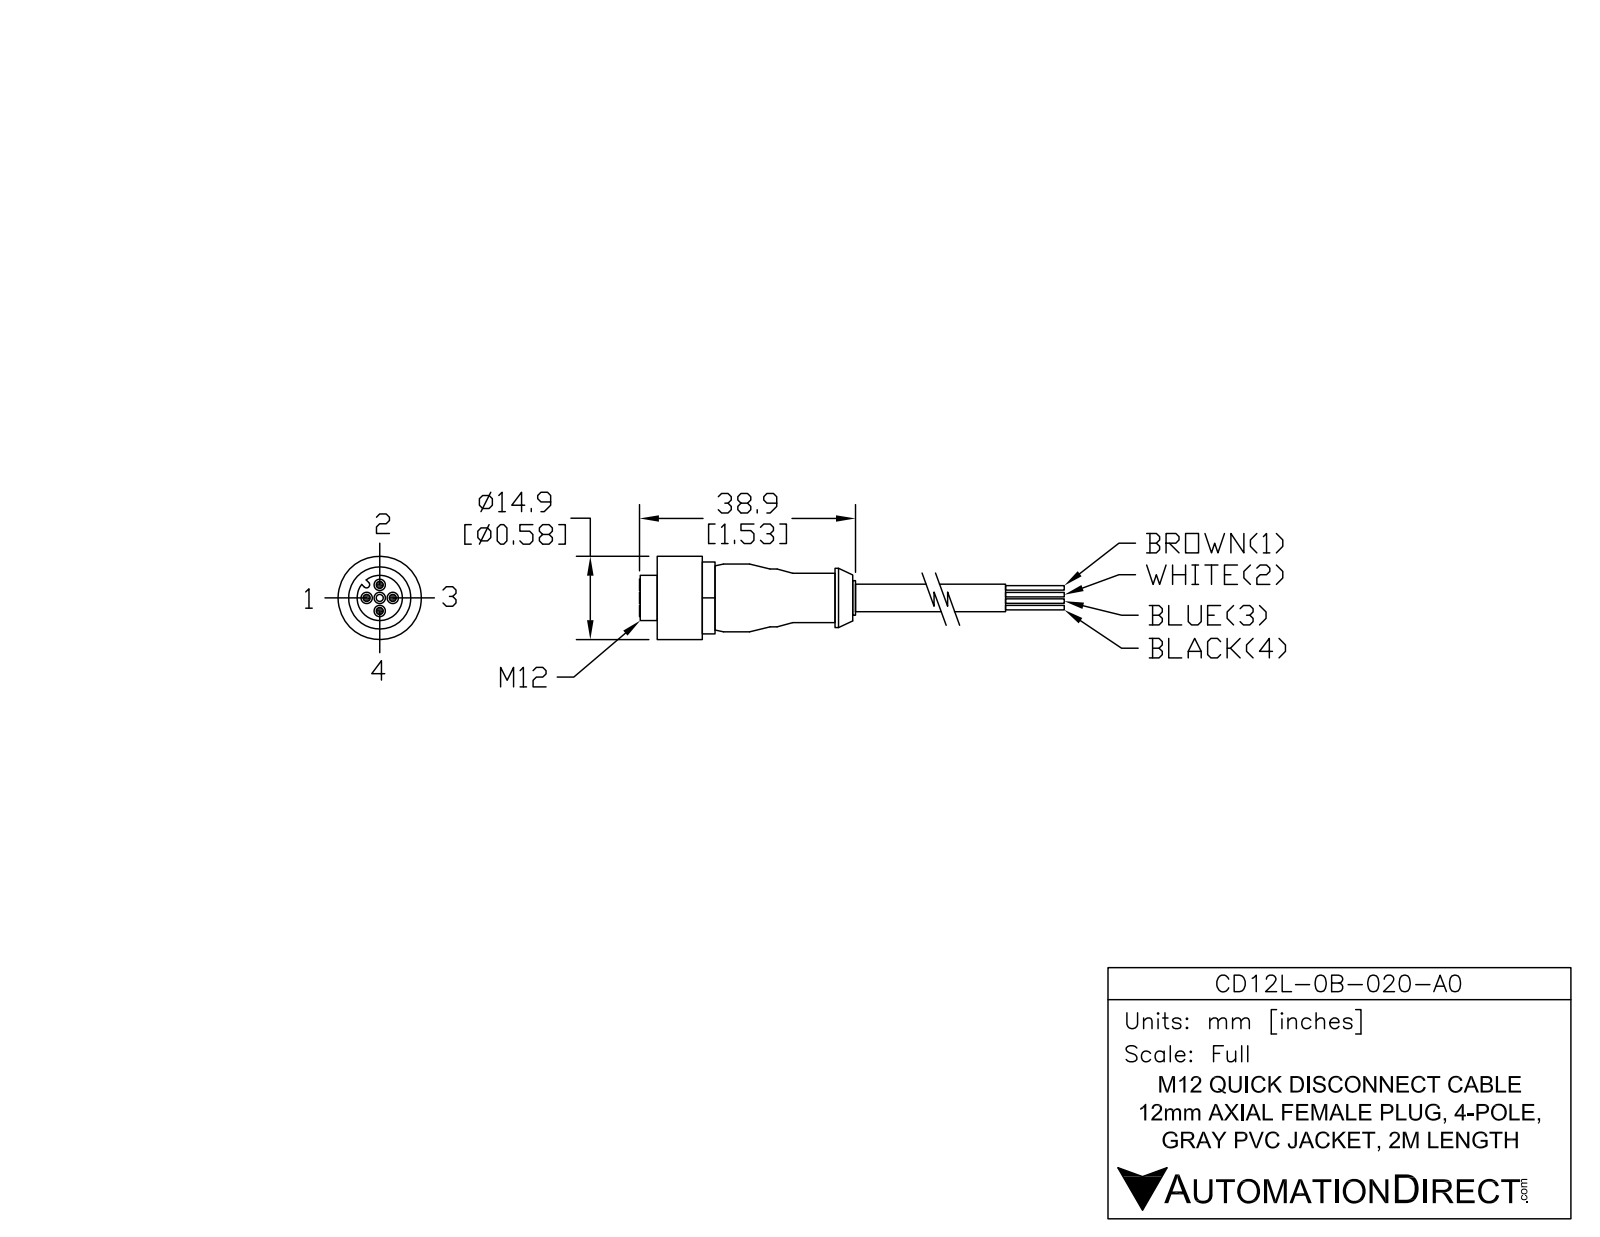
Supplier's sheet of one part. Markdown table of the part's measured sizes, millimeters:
| quantity | value |
| --- | --- |
| part name | CD12L-0B-020-A0 |
| STEP written by | SolidWorks 2017 (AUTOMOTIVE_DESIGN) |
| units | millimeters |
| bodies | 4 solids, 308 faces (195 planar, 107 cylindrical, 6 other) |
| overall size | 138.9 × 15 × 15 |
| volume | 5 509 mm³ |
| surface area | 4 482 mm² |
| round holes (diameter × count) | 1 × 5, 8.5 × 1, 12 × 1 |
| round bosses / shafts (diameter × count) | 12.2 × 1, 10.7 × 1, 10.4 × 1, 8.9 × 1, 8.1 × 1, 4.9 × 1 |
| partial cylindrical surfaces (radius × count) | 0.55 × 1, 7.5 × 1 |
| main face-to-face distances | 25.3, 1.4, 1.7, 8.2, 26.7, 37.2, 11.9, 10.5, 6.5, 30.7 |
| hole center spacings | 2.35, 3.32, 4.7 |
